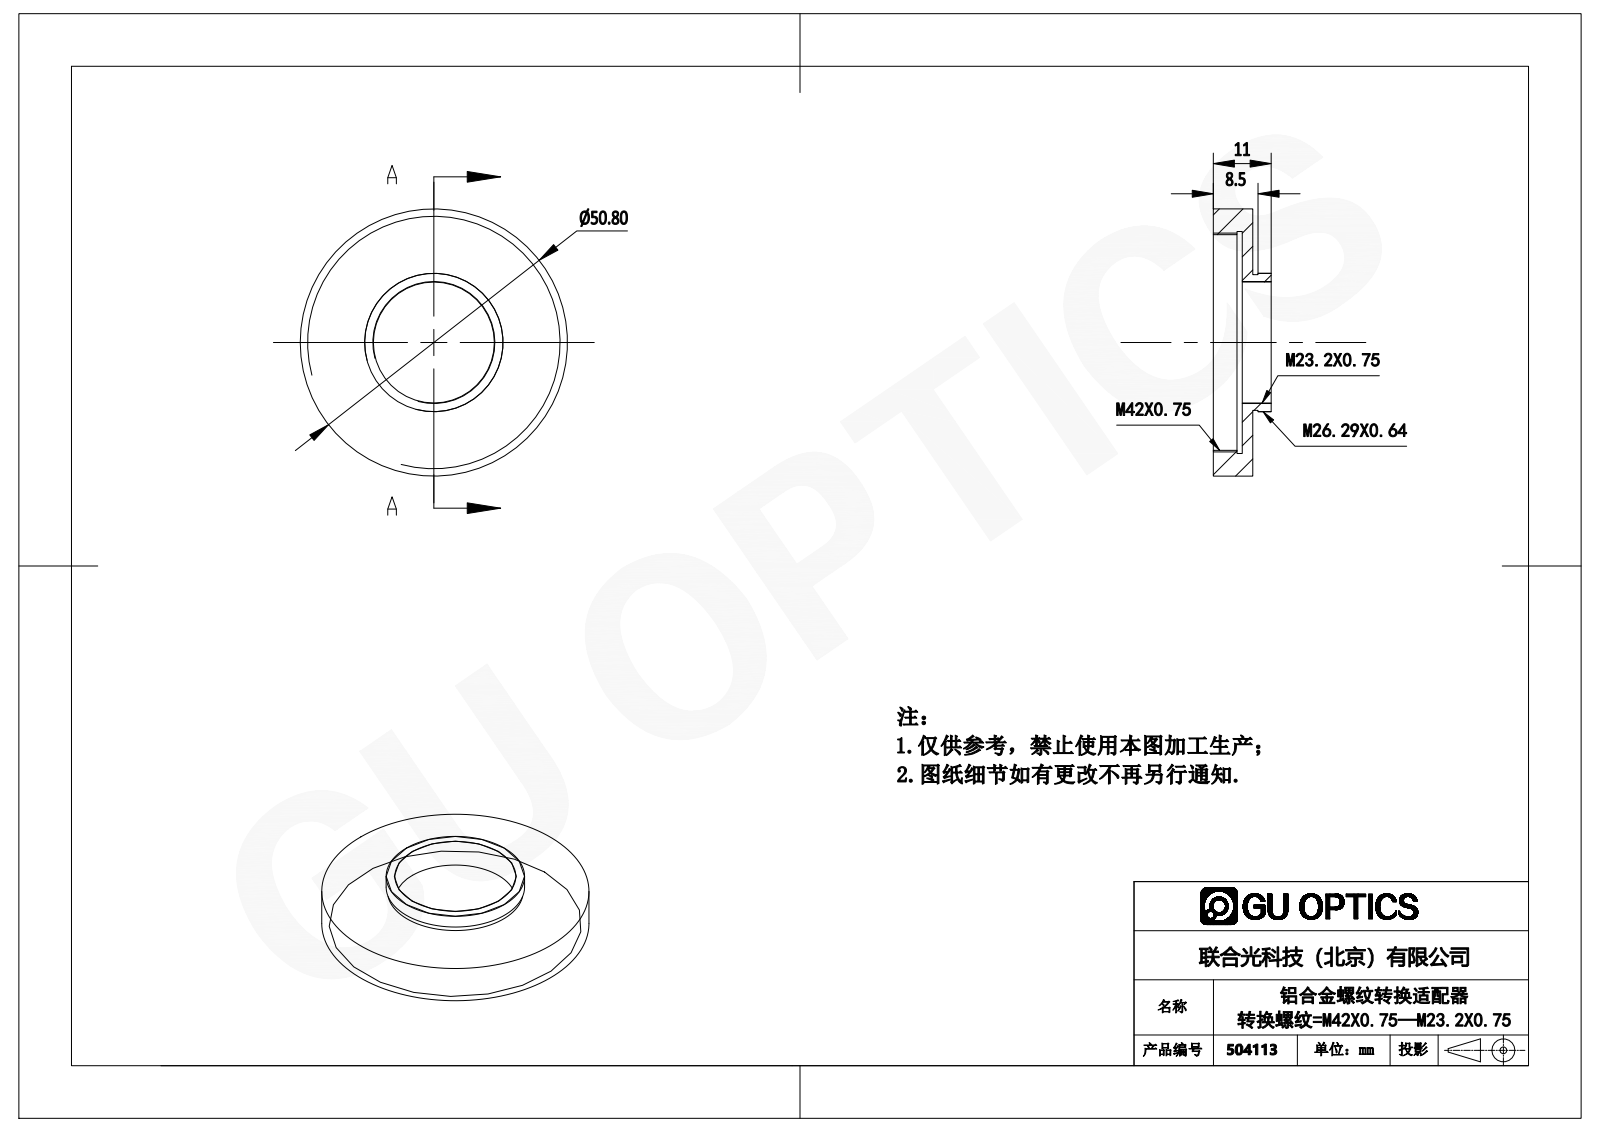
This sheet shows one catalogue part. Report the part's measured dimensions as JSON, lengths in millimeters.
{"part_name": "504113", "step_written_by": "SolidWorks 2016 (AUTOMOTIVE_DESIGN)", "units": "millimeters", "bodies": {"solids": 1, "faces": 18, "planar": 6, "cylindrical": 12, "other": 0}, "overall_size": [50.8, 50.8, 11], "volume_mm3": 7459, "surface_area_mm2": 6016, "round_holes": [[23, 1], [41, 1], [42.2, 1]], "round_bosses_or_shafts": [[50.8, 1], [26.32, 1], [25.8, 1]], "face_to_face_distances": [2, 5.5, 7.5, 11, 3.5, 1, 3, 4.5, 6.5, 8.5]}
